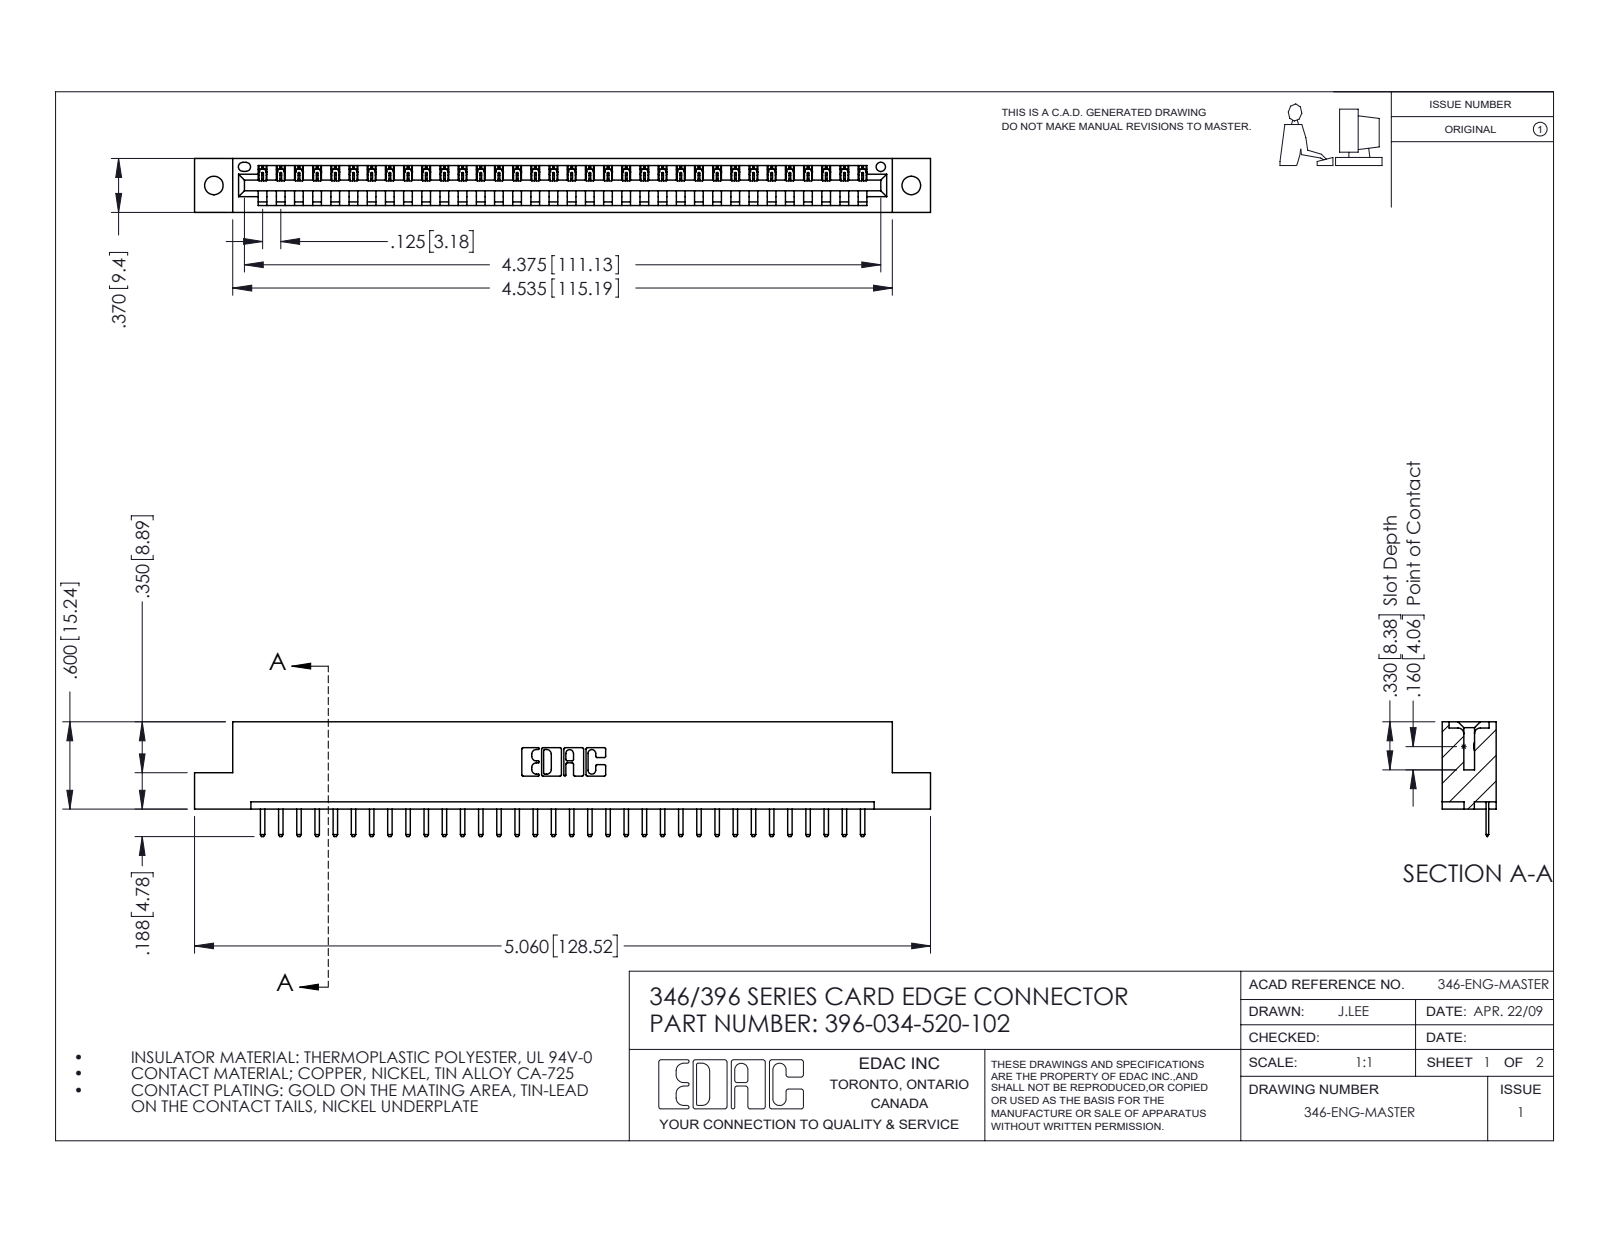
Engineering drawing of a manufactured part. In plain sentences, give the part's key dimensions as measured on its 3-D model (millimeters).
The part is named "346 Part_Flush Mounting Lugs - 0.128 Dia; 345-292-001_345-293-120; 396-034-520-102". Its 3-D file was written by "SolidWorks 2016 (CONFIG_CONTROL_DESIGN)". It is 35 solids with 2230 faces: 1504 planar, 726 cylindrical and 0 other. Overall it measures 128.5 by 20 by 9.4 millimeters. Its volume is 12 100 cubic millimeters and its surface area 14 460 square millimeters. Round holes: 2 of diameter 3.3, 1 of diameter 1.6. Partial cylindrical surfaces (rounded edges, fillets, slot ends): 70 of radius 0.3, 68 of radius 0.2, 22 of radius 0.3, 6 of radius 0.2, 6 of radius 0.8, 3 of radius 0.7, 2 of radius 0.8, 2 of radius 1. The main face-to-face distances are 1.2, 8.2, 9.4, 6.4, 3.8, 5.6, 2.5, 4.4, 1.8, 7.6. The hole center spacings are 6.2, 116.5, 121.8.
